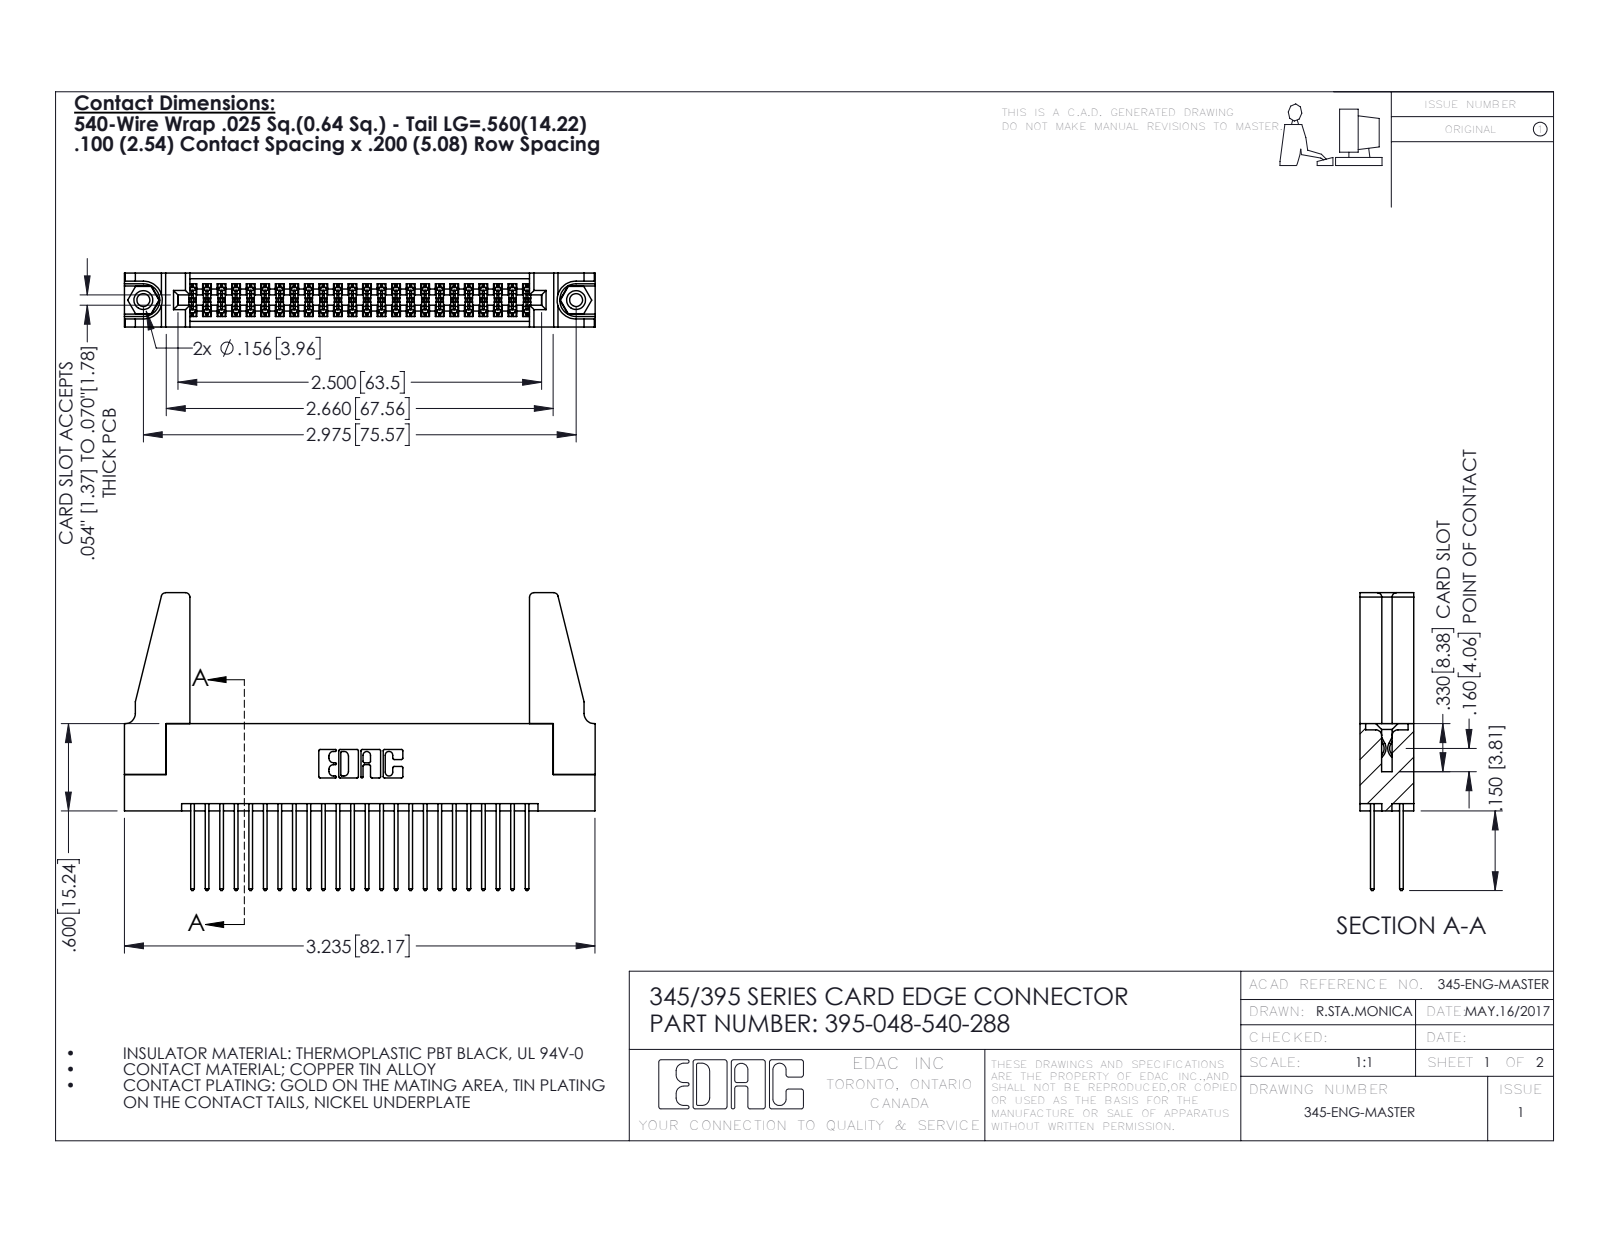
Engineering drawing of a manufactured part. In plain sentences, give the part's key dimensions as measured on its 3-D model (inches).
The part is named "345 Part_Flush Mounting Lugs - 0.156 Dia-TH; 345-220-078_345-220-088; 345-292-001_345-293-140; 345-250-001_345-250-001-102 (+1 more)". Its 3-D file was written by "SolidWorks 2016 (CONFIG_CONTROL_DESIGN)". It is 53 solids with 2650 faces: 1736 planar, 898 cylindrical and 16 other. Overall it measures 3.236 by 2.047 by 0.37 inches. Its volume is 0.687 cubic inches and its surface area 23.94 square inches. Round holes: 2 of diameter 0.089, 2 of diameter 0.125, 2 of diameter 0.156, 1 of diameter 0.064. Round bosses or shafts: 2 of diameter 0.155. Partial cylindrical surfaces (rounded edges, fillets, slot ends): 72 of radius 0.006, 48 of radius 0.01, 22 of radius 0.01, 8 of radius 0.03, 6 of radius 0.007, 6 of radius 0.031, 3 of radius 0.026, 2 of radius 0.014. The main face-to-face distances are 0.072, 0.298, 0.2, 0.37, 0.098, 0.272, 0.025, 0.225, 0.175, 0.149. The hole center spacings are 0.27, 2.741, 2.975.
